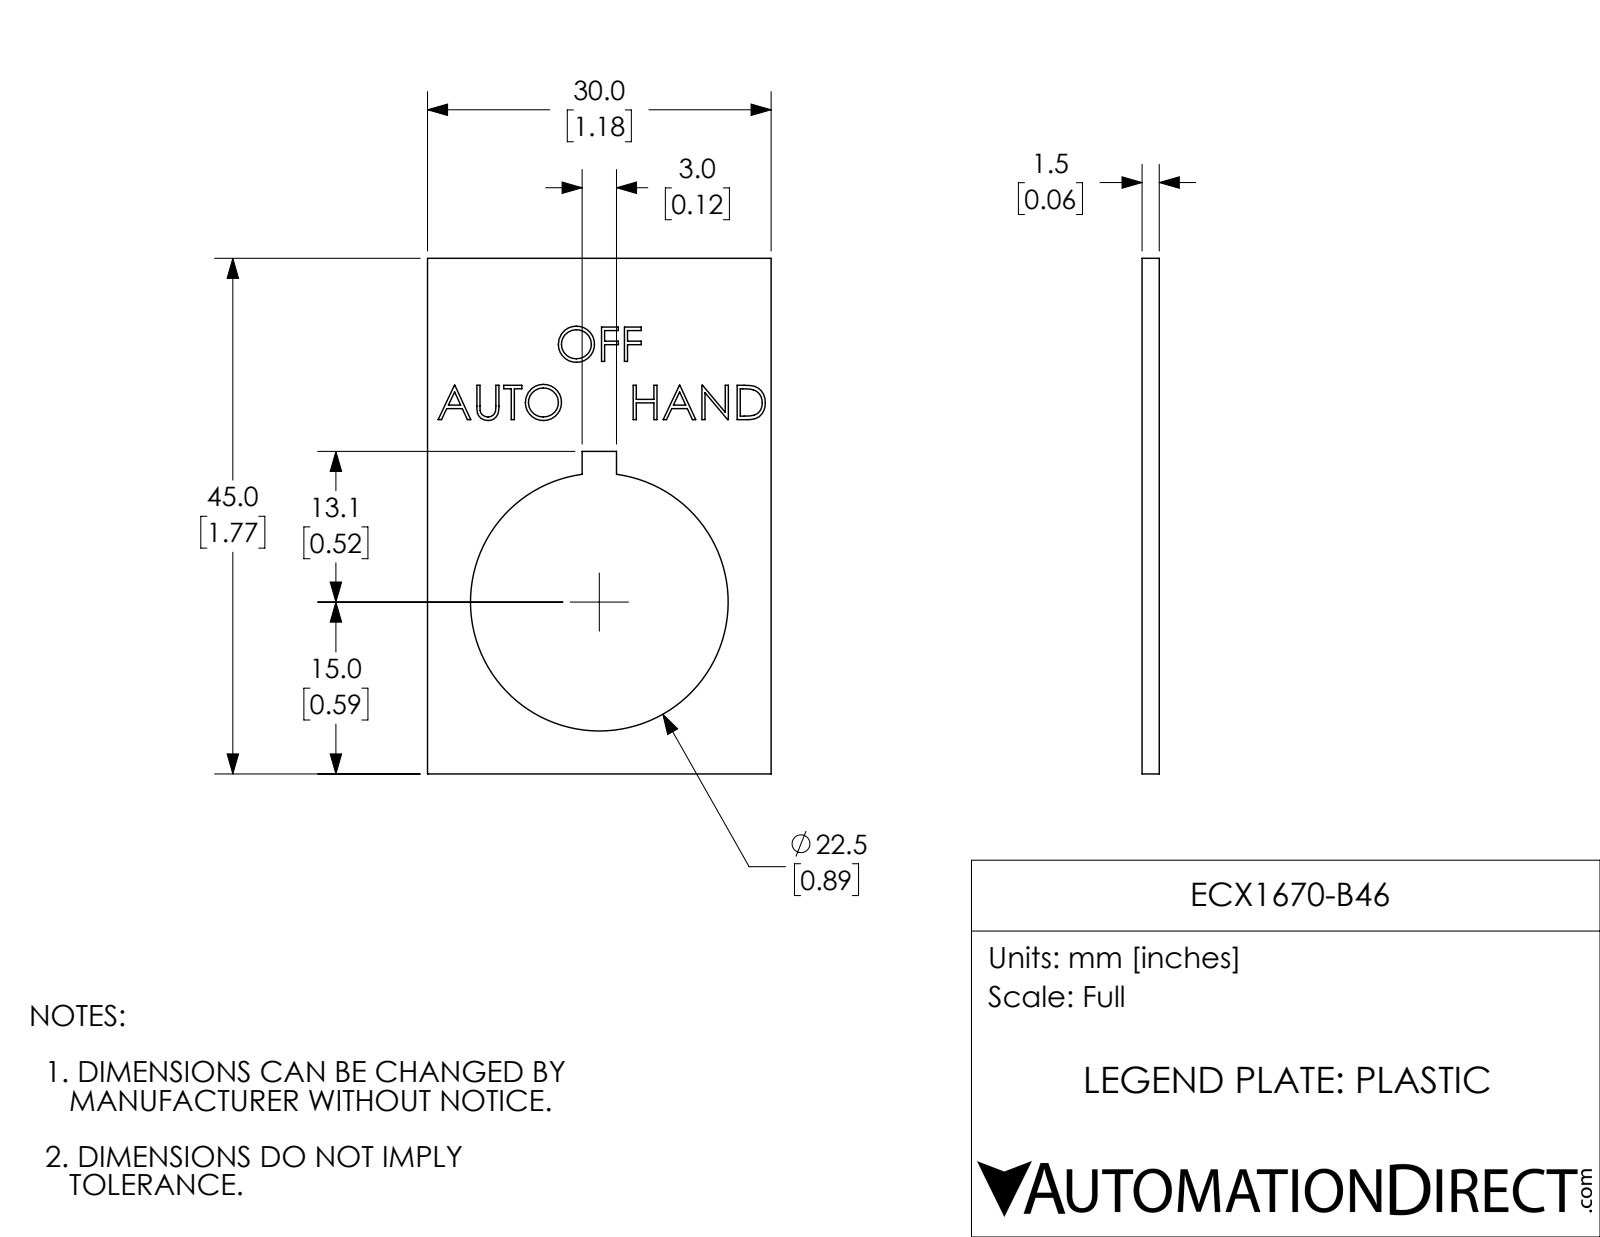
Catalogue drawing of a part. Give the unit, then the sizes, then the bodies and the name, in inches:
Units: inches
Overall size (bounding box): 1.772 × 1.181 × 0.059
Round holes (diameter × count): ⌀0.886 ×1
Main face-to-face distances: 0.059, 1.181, 1.772, 0.058, 0.531, 0.65, 1.108, 0.663, 0.118, 0.012
Volume: 0.087 in³ · Surface area: 3.463 in²
Bodies: 1 solid, 142 faces (109 planar, 3 cylindrical, 30 other)
Part name (STEP PRODUCT): ECX1670-B46
STEP written by: SolidWorks 2017 (AUTOMOTIVE_DESIGN)
